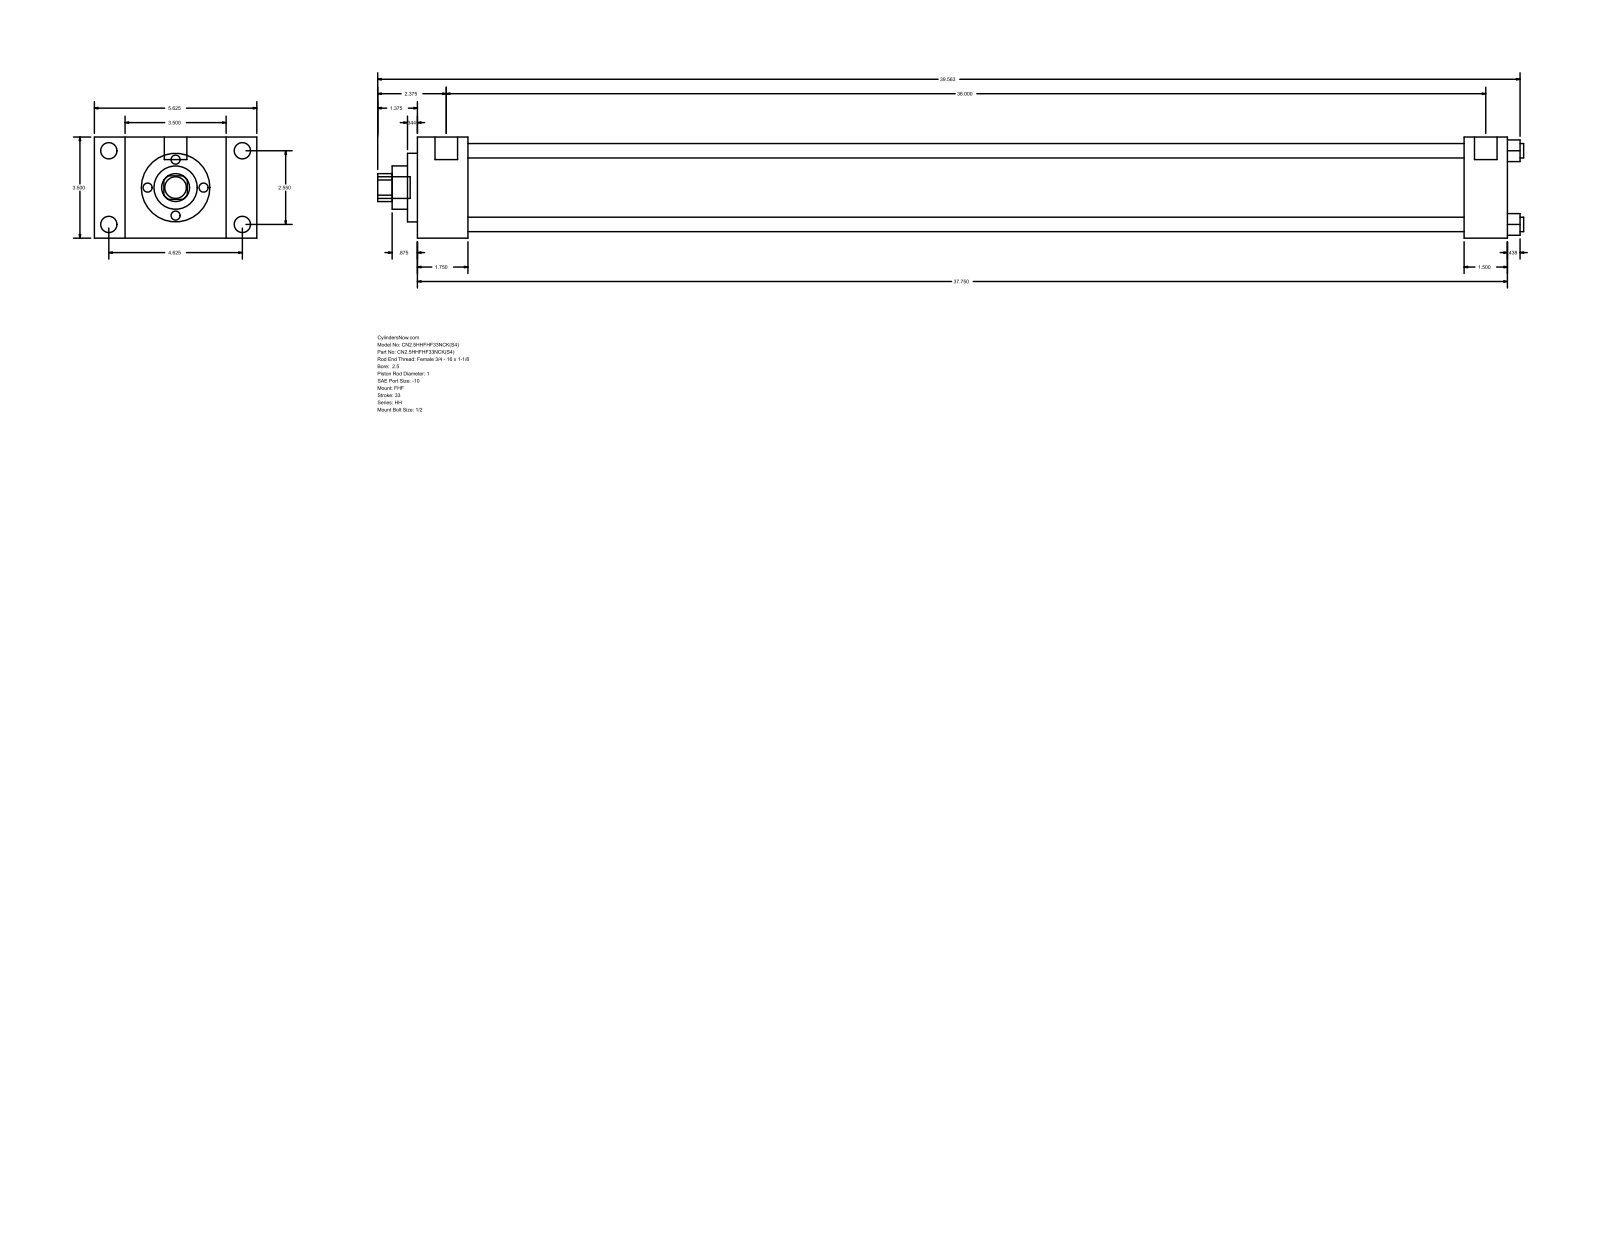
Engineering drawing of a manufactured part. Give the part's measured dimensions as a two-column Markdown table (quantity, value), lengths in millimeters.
| quantity | value |
| --- | --- |
| part name | HH_FHF__0250_1 |
| STEP written by | GSSL Pune (CONFIG_CONTROL_DESIGN) |
| units | millimeters |
| bodies | 0 solids, 90 faces (61 planar, 29 cylindrical, 0 other) |
| overall size | 1008.06 × 142.88 × 88.9 |
| round holes (diameter × count) | 12.7 × 4, 25.4 × 1, 38.1 × 1, 60.33 × 1, 73.03 × 1 |
| round bosses / shafts (diameter × count) | 14.3 × 4, 5.56 × 4, 19.84 × 2, 19.05 × 1 |
| partial cylindrical surfaces (radius × count) | 12.29 × 1 |
| main face-to-face distances | 88.9, 44.46, 26.99, 115.89, 958.85, 914.39, 142.88, 920.75, 876.29, 38.1 |
| hole center spacings | 45.79, 64.76, 91.58 |
